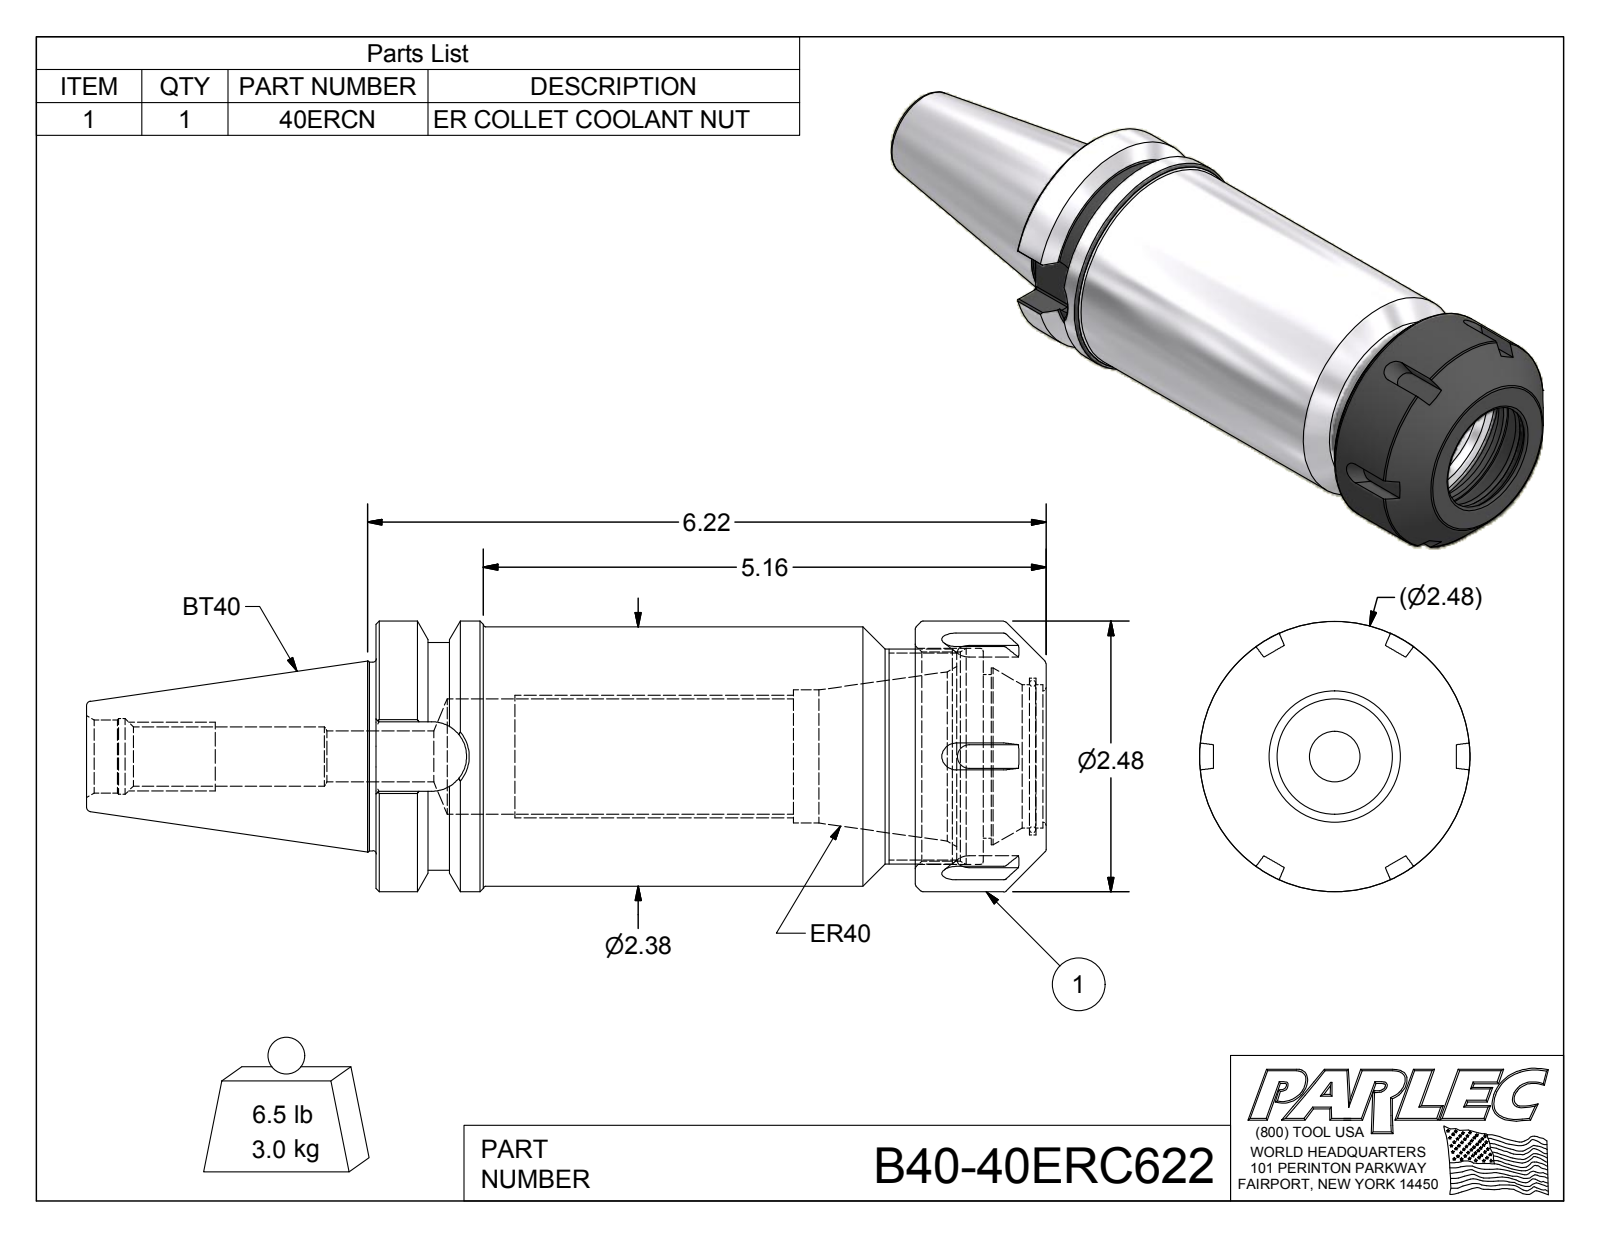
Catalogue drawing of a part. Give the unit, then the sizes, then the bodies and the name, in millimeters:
Units: millimetres
Overall size (bounding box): 223.4 × 63 × 63
Round holes (diameter × count): ⌀11.8 ×1, ⌀13.8 ×1, ⌀17 ×1, ⌀17.6 ×1, ⌀26.8 ×1, ⌀31 ×1, ⌀33.4 ×1, ⌀36.5 ×1, ⌀38.1 ×1, ⌀41.1 ×1, ⌀48.7 ×1, ⌀50.3 ×1
Round bosses / shafts (diameter × count): ⌀63 ×1, ⌀63 ×1, ⌀60.3 ×1, ⌀53 ×1, ⌀50 ×1, ⌀43.9 ×1
Partial cylindrical surfaces — rounded edges, fillets, slot ends (radius × count): R0.5 ×8, R8.1 ×1
Main face-to-face distances: 141.4, 156, 14.6, 125.5, 15.9, 30.5, 135.2, 9.7, 6.2, 20.8
Volume: 376 400 mm³ · Surface area: 66 450 mm²
Bodies: 2 solids, 131 faces (50 planar, 32 cylindrical, 49 other)
Part name (STEP PRODUCT): B40-40ERC622; B40-40ER6-1; 40ERCN
STEP written by: Autodesk Inventor 2012 (AUTOMOTIVE_DESIGN)
